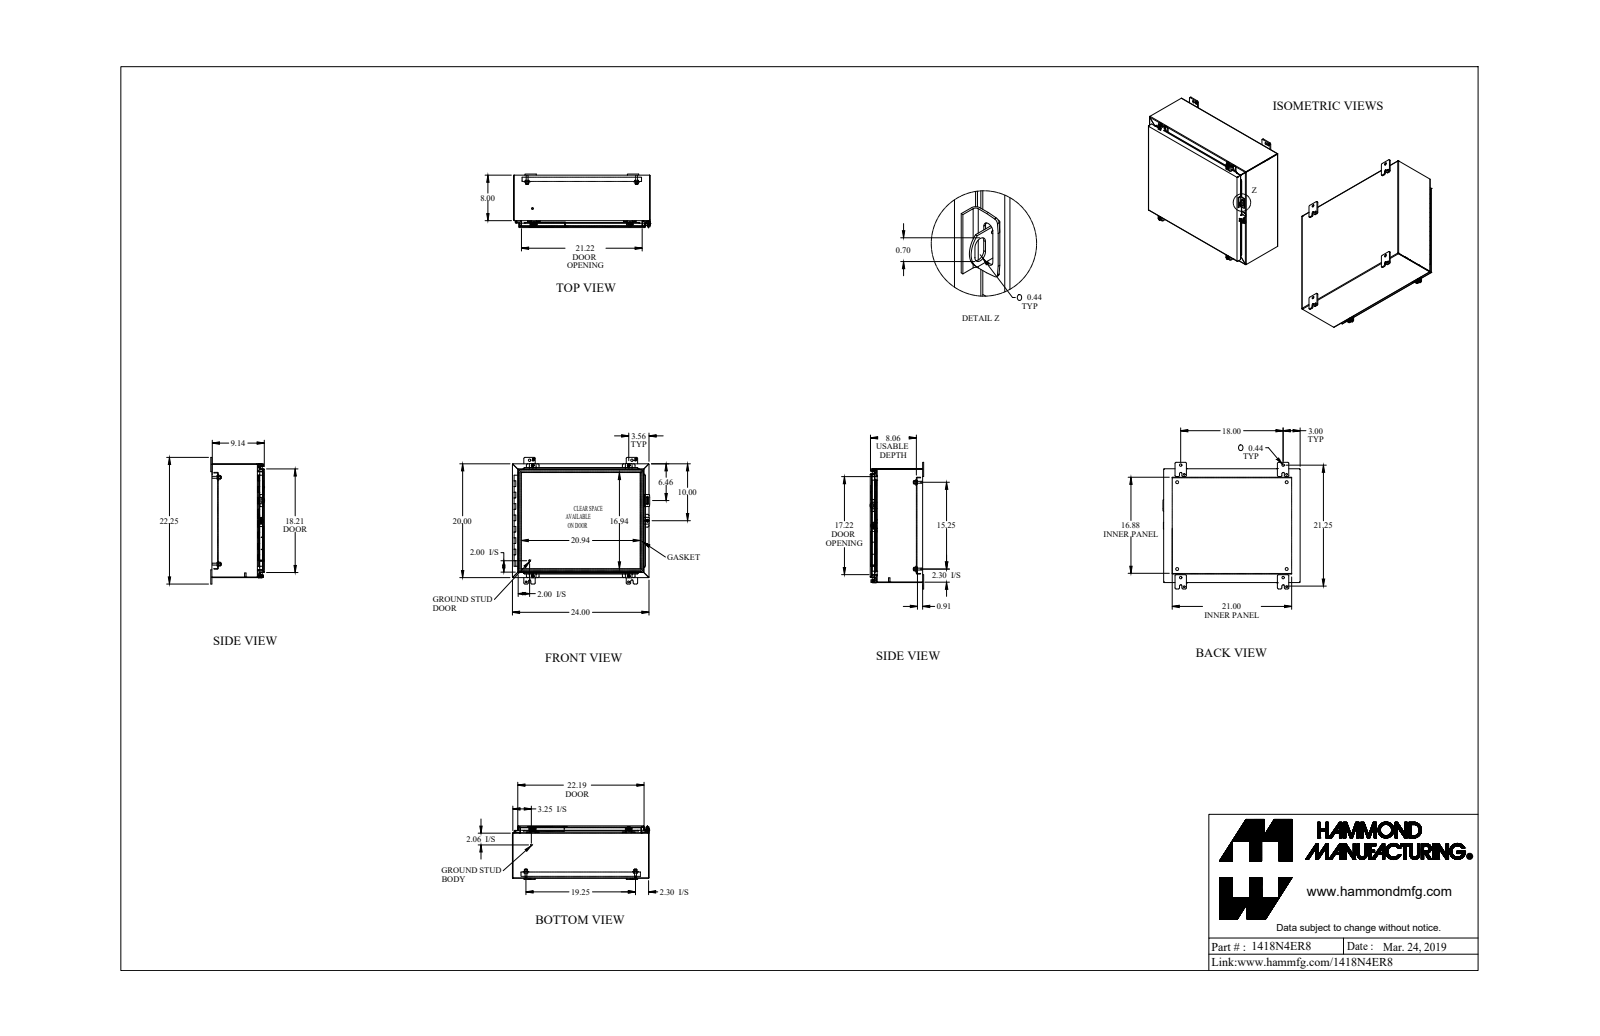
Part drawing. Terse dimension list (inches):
name: 1418N4ER8_Default
written by: SolidWorks 2019 (CONFIG_CONTROL_DESIGN)
unit: in
bodies: 44 solids, 1515 faces (927 planar, 500 cylindrical, 88 other)
size: 24.126 × 22.25 × 9.437
volume: 185.7 in³; area: 4 864 in²
holes: 5× ⌀0.213, 5× ⌀0.375, 4× ⌀0.265, 4× ⌀0.313, 4× ⌀0.437, 4× ⌀0.5, 2× ⌀0.307, 2× ⌀0.445, 1× ⌀0.125, 1× ⌀0.187, 1× ⌀0.265
bosses: 5× ⌀0.5, 5× ⌀0.39, 5× ⌀0.244, 4× ⌀0.65, 4× ⌀0.375, 4× ⌀0.33, 2× ⌀1, 2× ⌀0.281
rounds: 26× R0.188, 24× R0.036, 24× R0.108, 24× R0.25, 21× R0.048, 21× R0.143, 10× R0.125, 10× R0.141
face distances: 0.072, 0.072, 9.066, 9.138, 9.138, 9.21, 0.095, 19.928, 8.106, 8.034
hole spacings: 2.434, 24.559, 17.416, 18.187, 3.065, 18, 25.063, 26.722
